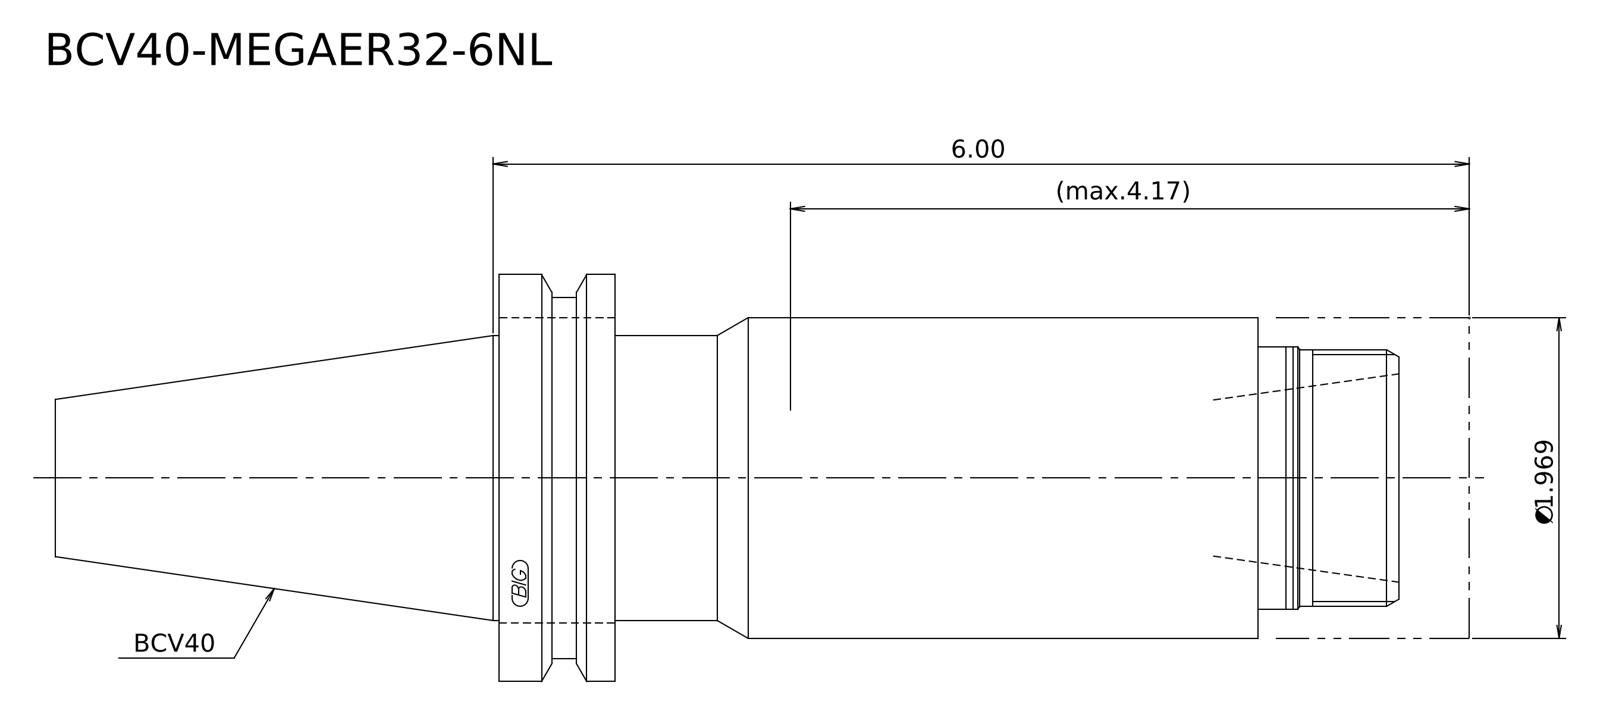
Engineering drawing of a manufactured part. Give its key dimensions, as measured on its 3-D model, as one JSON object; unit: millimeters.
{"part_name": "BCV40-MEGAER32-6", "step_written_by": "CREO PARAMETRIC BY PTC INC, 2016380 (AUTOMOTIVE_DESIGN)", "units": "millimeters", "bodies": {"solids": 1, "faces": 63, "planar": 25, "cylindrical": 28, "other": 10}, "overall_size": [209.65, 63.5, 61.35], "volume_mm3": 275897, "surface_area_mm2": 47010, "round_holes": [[9.53, 1], [13.6, 1], [16.32, 1], [20.3, 1], [24.8, 1]], "round_bosses_or_shafts": [[63.5, 1], [56.36, 1], [50, 1], [44.45, 1], [41, 1], [40, 1]], "face_to_face_distances": [18.05, 100.35, 118.4, 22, 122.35, 140.4, 209.65, 187.65, 87.3, 69.25]}
